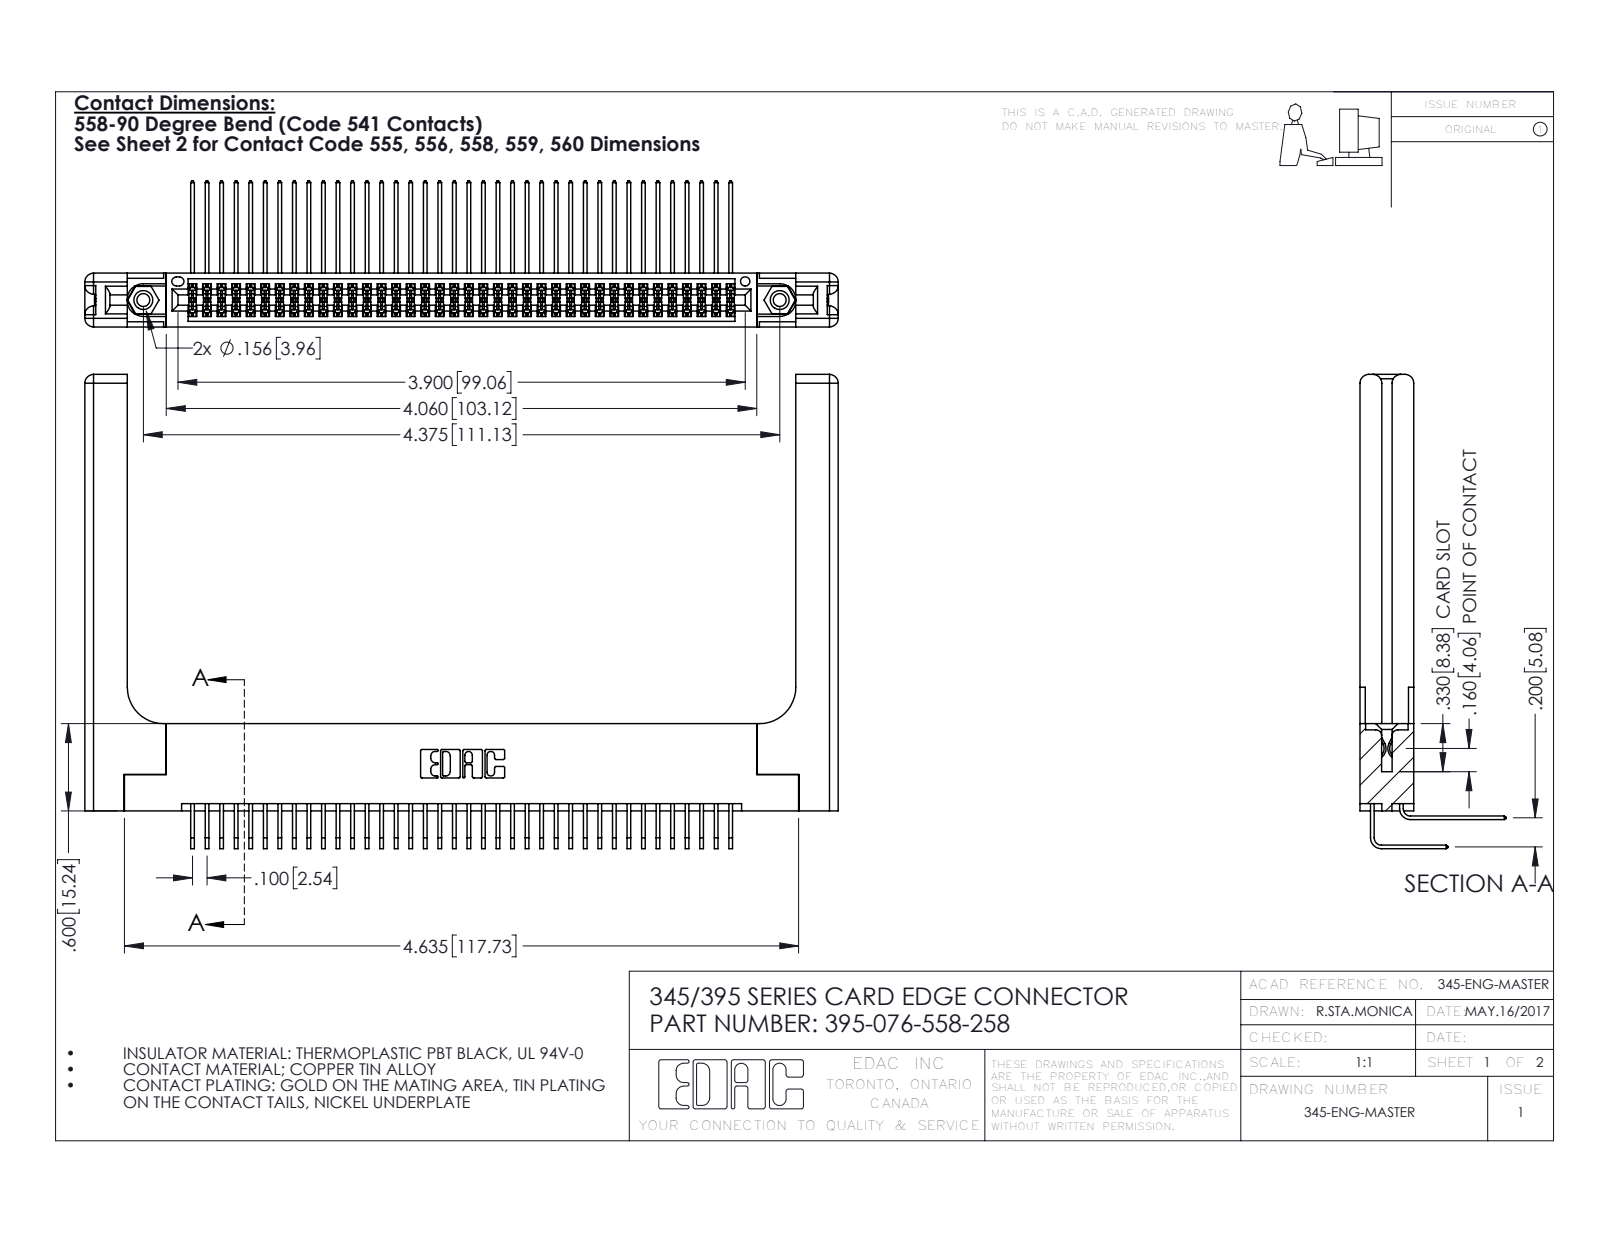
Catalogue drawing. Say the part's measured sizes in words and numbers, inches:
The part is named "345-220-058_345-220-058; 345 Part_Flush Mounting Lugs - 0.156 Dia-TH; 345-292-001_558 559 Tail - 1; 345-292-001_558 Tail - 2 (+2 more)". Its 3-D file was written by "SolidWorks 2016 (CONFIG_CONTROL_DESIGN)". It is 81 solids with 4334 faces: 2888 planar, 1386 cylindrical and 60 other. Overall it measures 5.179 by 3.259 by 1.005 inches. Its volume is 1.321 cubic inches and its surface area 41.11 square inches. Round holes: 2 of diameter 0.089, 2 of diameter 0.125, 2 of diameter 0.156, 1 of diameter 0.064. Round bosses or shafts: 2 of diameter 0.155. Partial cylindrical surfaces (rounded edges, fillets, slot ends): 114 of radius 0.006, 22 of radius 0.01, 16 of radius 0.06, 6 of radius 0.007, 6 of radius 0.031, 3 of radius 0.026, 2 of radius 0.014, 2 of radius 0.019. The main face-to-face distances are 0.072, 0.37, 0.298, 0.2, 0.098, 0.272, 0.025, 0.225, 0.148, 0.15. The hole center spacings are 0.27, 4.139, 4.375.
